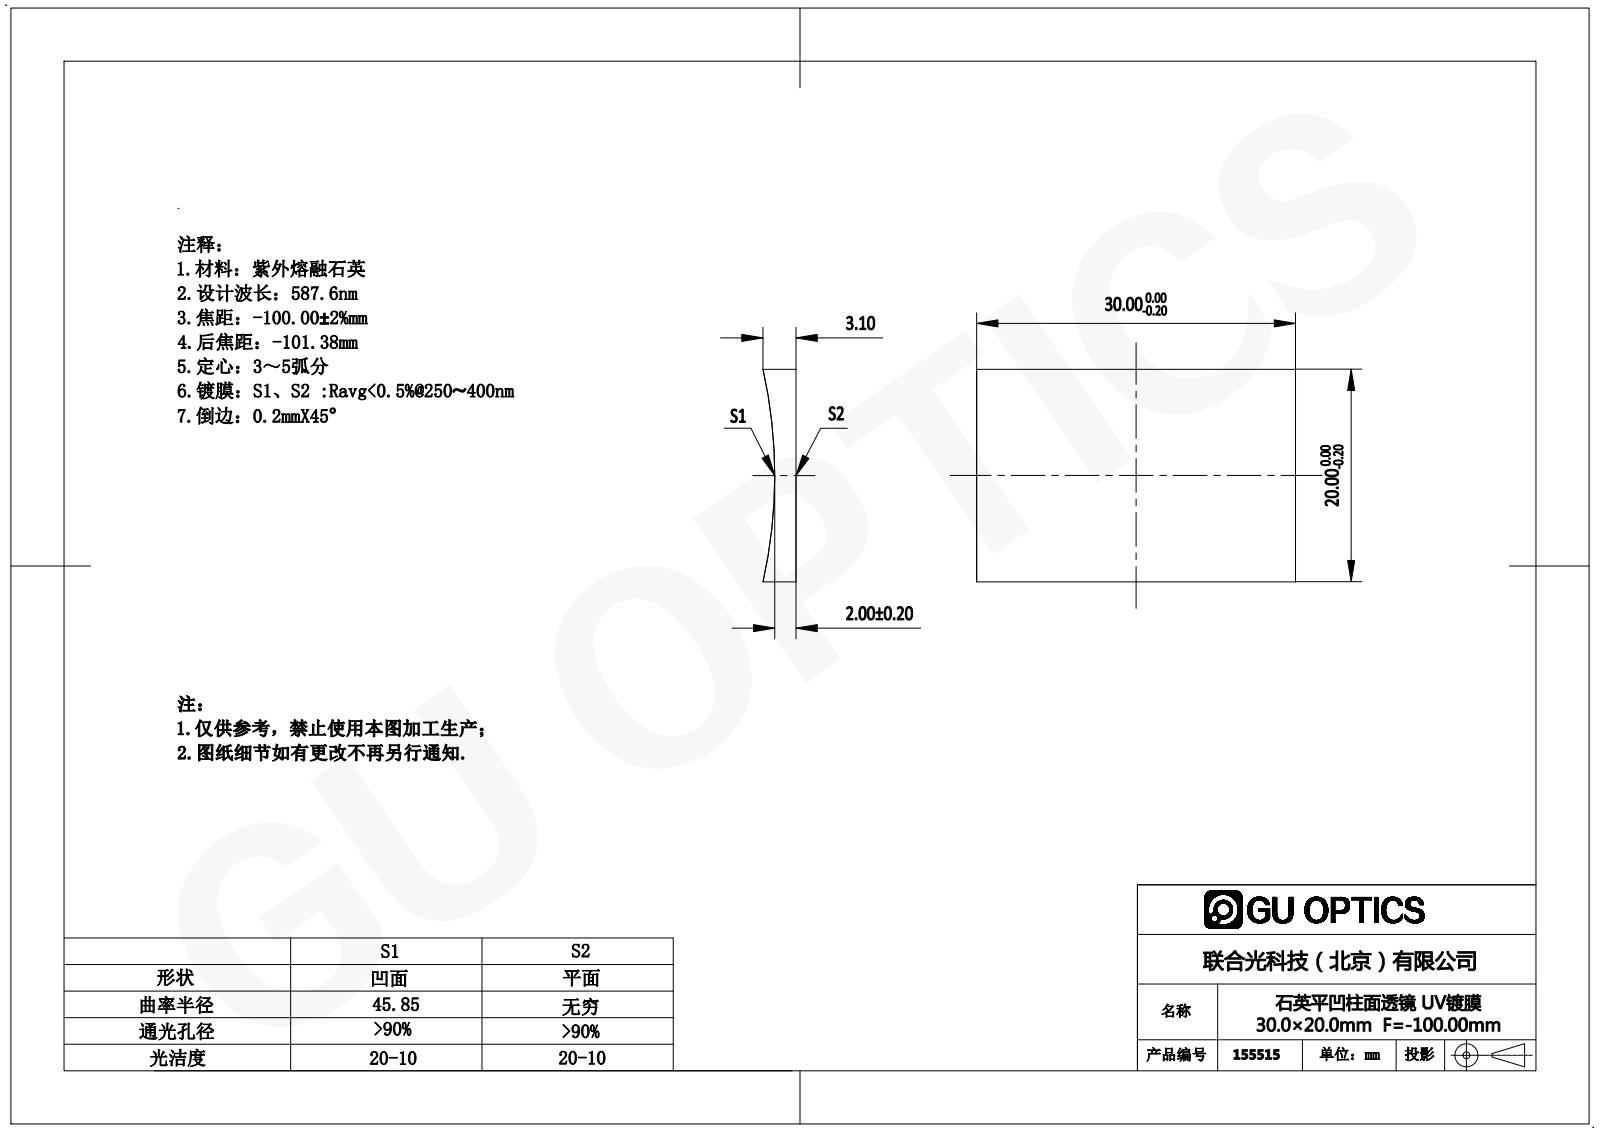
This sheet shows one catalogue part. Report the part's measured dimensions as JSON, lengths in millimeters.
{"part_name": "155489", "step_written_by": "SolidWorks 2016 (AUTOMOTIVE_DESIGN)", "units": "millimeters", "bodies": {"solids": 1, "faces": 6, "planar": 5, "cylindrical": 1, "other": 0}, "overall_size": [30, 20, 3.1], "volume_mm3": 1420, "surface_area_mm2": 1486, "partial_cylinders_radius": [[45.85, 1]], "face_to_face_distances": [20, 30]}
